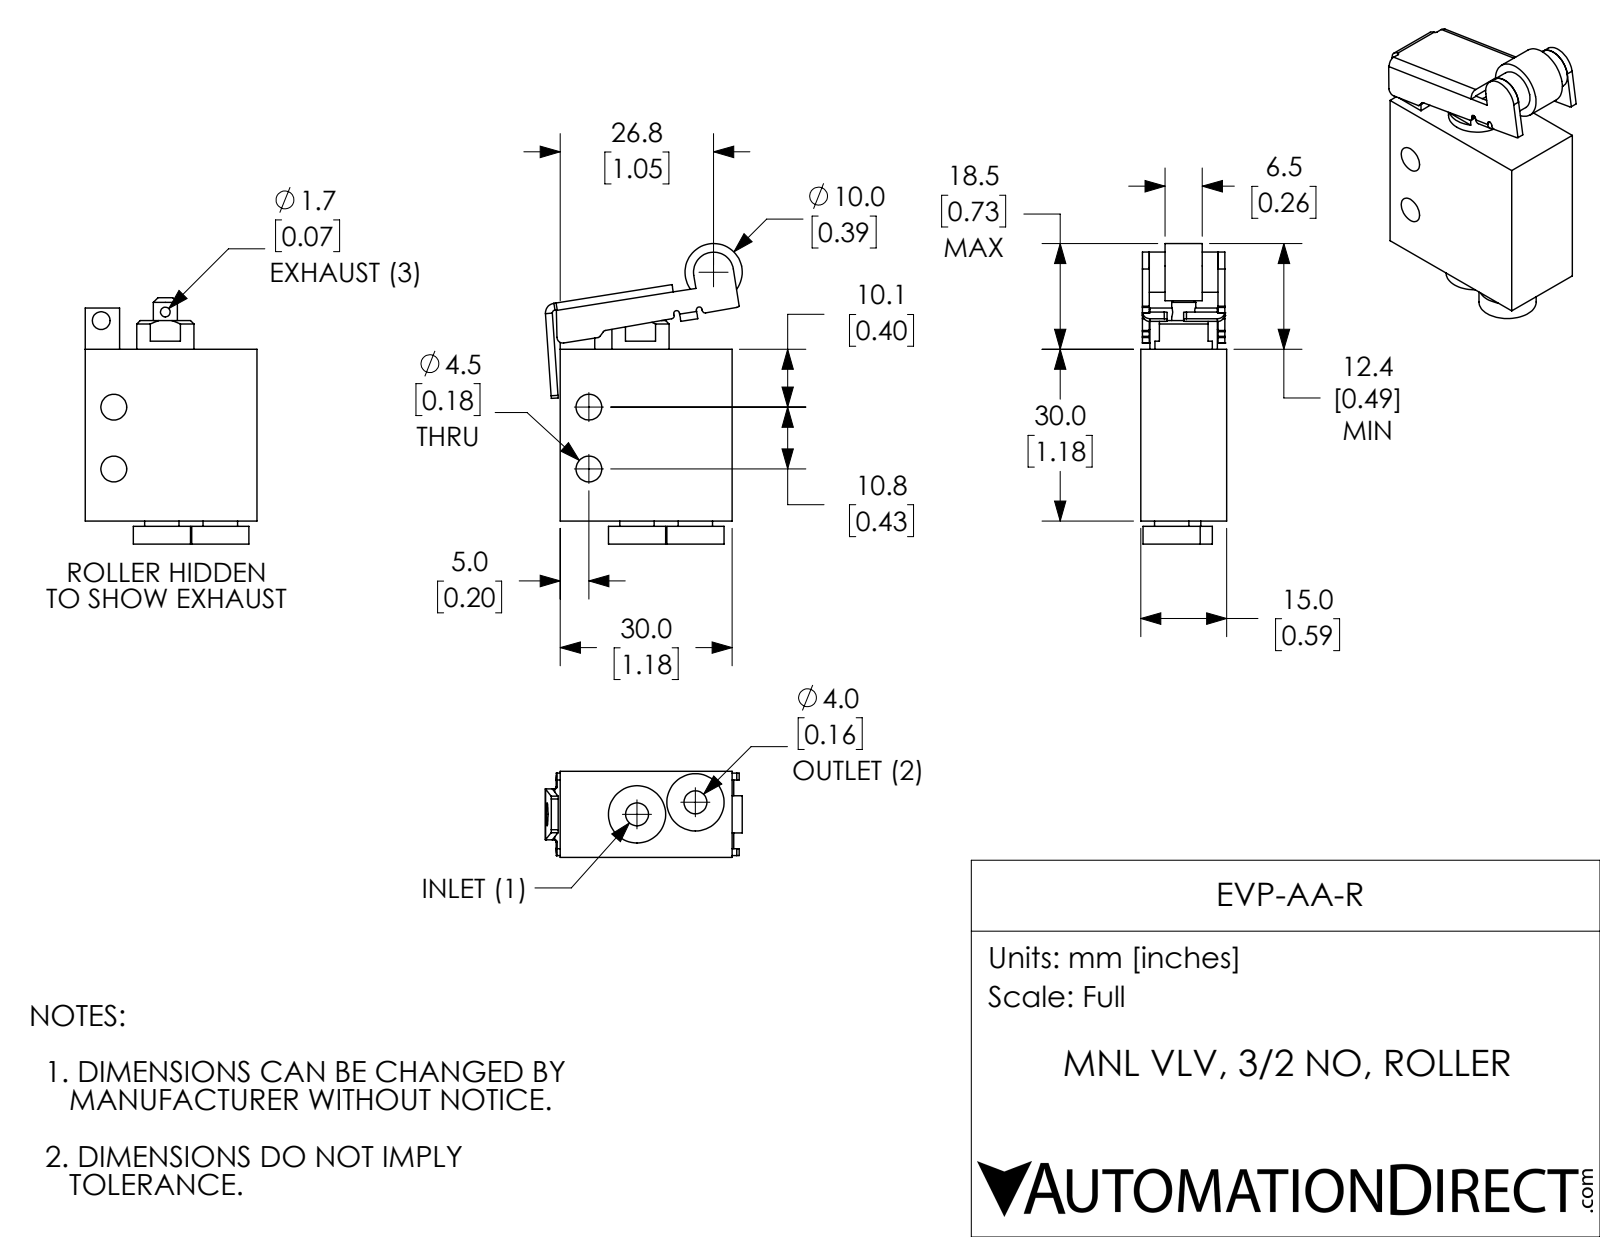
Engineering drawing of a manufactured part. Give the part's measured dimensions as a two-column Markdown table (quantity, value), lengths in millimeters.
| quantity | value |
| --- | --- |
| part name | EVP-AA-R |
| STEP written by | SolidWorks 2017 (AUTOMOTIVE_DESIGN) |
| units | millimeters |
| bodies | 3 solids, 148 faces (74 planar, 70 cylindrical, 4 other) |
| overall size | 52.5 × 34.4 × 15 |
| volume | 16 300 mm³ |
| surface area | 7 684 mm² |
| round holes (diameter × count) | 4 × 3, 4.5 × 2, 1.7 × 1, 3.1 × 1 |
| round bosses / shafts (diameter × count) | 10 × 4, 6 × 2, 7 × 1, 5 × 1, 4.2 × 1 |
| partial cylindrical surfaces (radius × count) | 0.5 × 13, 1.3 × 4, 0.1 × 2, 0.4 × 2, 1 × 2, 1.7 × 1 |
| main face-to-face distances | 15, 30, 1.2, 1.5, 13.5, 14.7, 13.2, 1.2, 12, 14.4 |
| hole center spacings | 10.4, 10.8, 11.3, 15.3, 18.9, 26, 28.8 |
